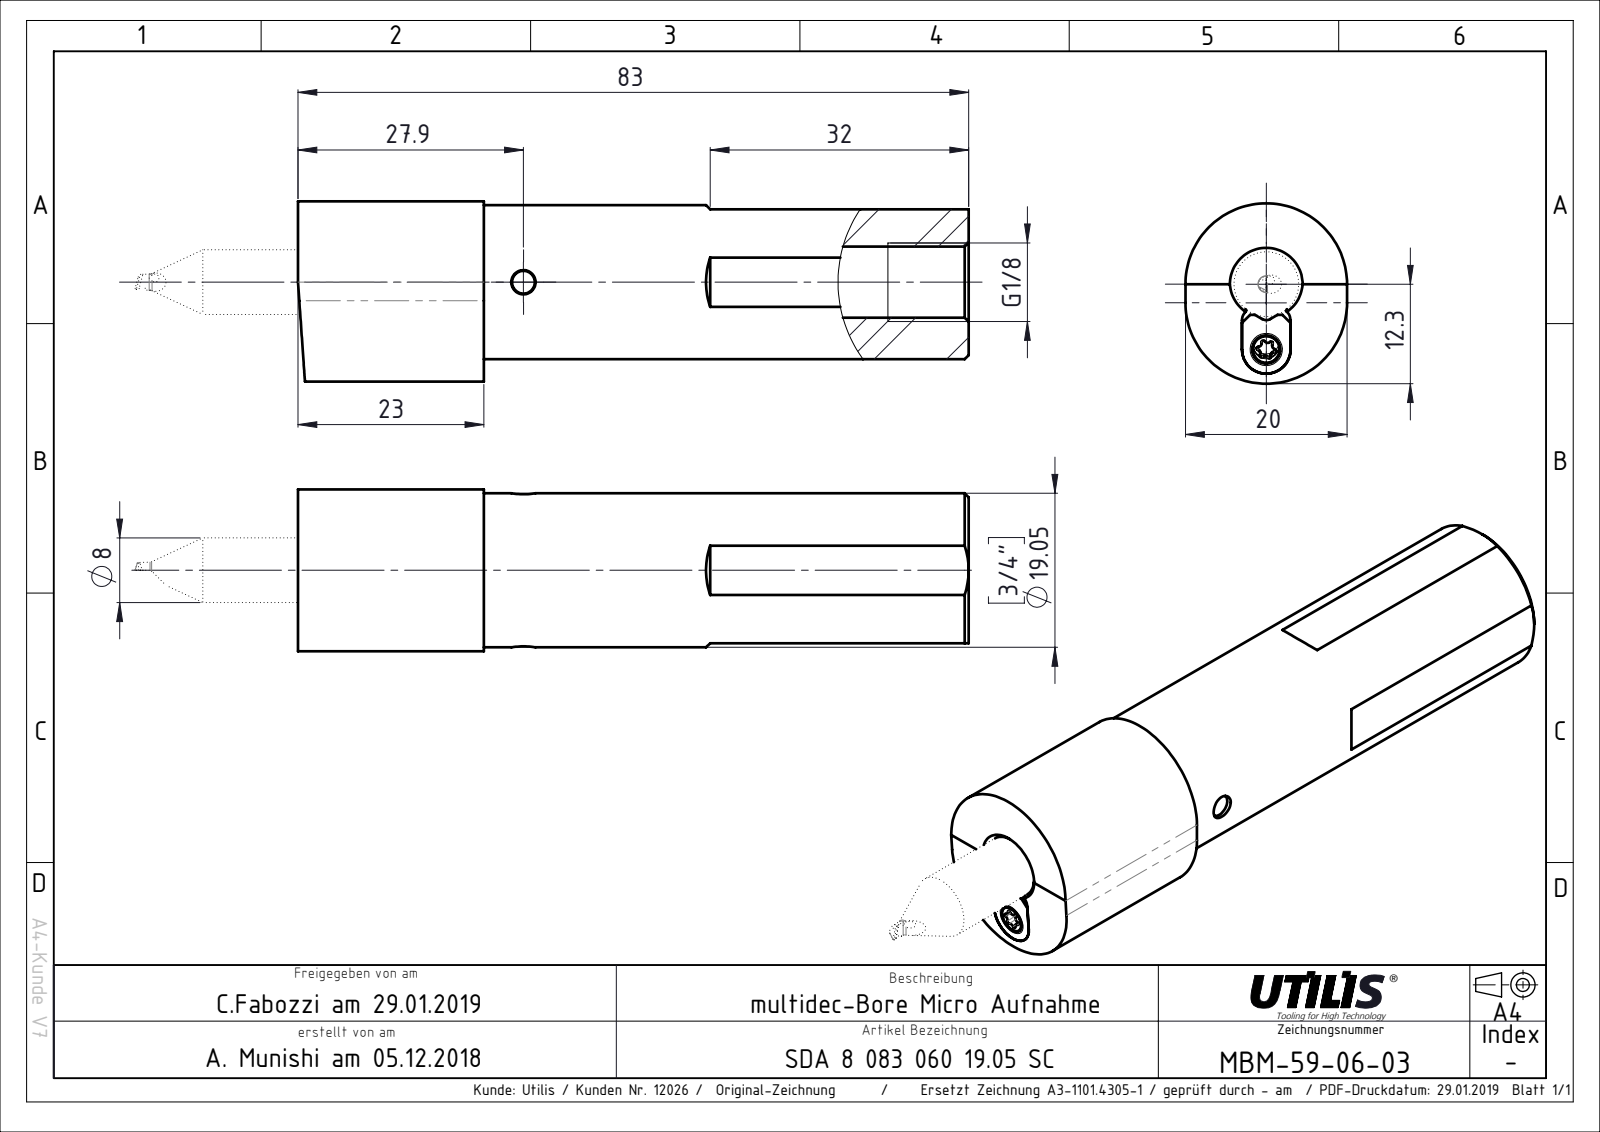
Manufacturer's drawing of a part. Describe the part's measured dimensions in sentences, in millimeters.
The part is named "MBM-59-06-03". Its 3-D file was written by "SolidWorks 2018 (CONFIG_CONTROL_DESIGN)". It is 1 solid with 45 faces: 13 planar, 16 cylindrical and 16 other. Overall it measures 83 by 22.3 by 20 millimeters. Its volume is 19 887 cubic millimeters and its surface area 8 220 square millimeters. Round holes: 1 of diameter 3, 1 of diameter 3.3, 1 of diameter 8, 1 of diameter 8.8. Round bosses or shafts: 1 of diameter 19.05. Partial cylindrical surfaces (rounded edges, fillets, slot ends): 2 of radius 10, 1 of radius 3. The main face-to-face distances are 83, 23, 60, 7, 13, 0.97, 19.03, 20, 6.03, 6.
